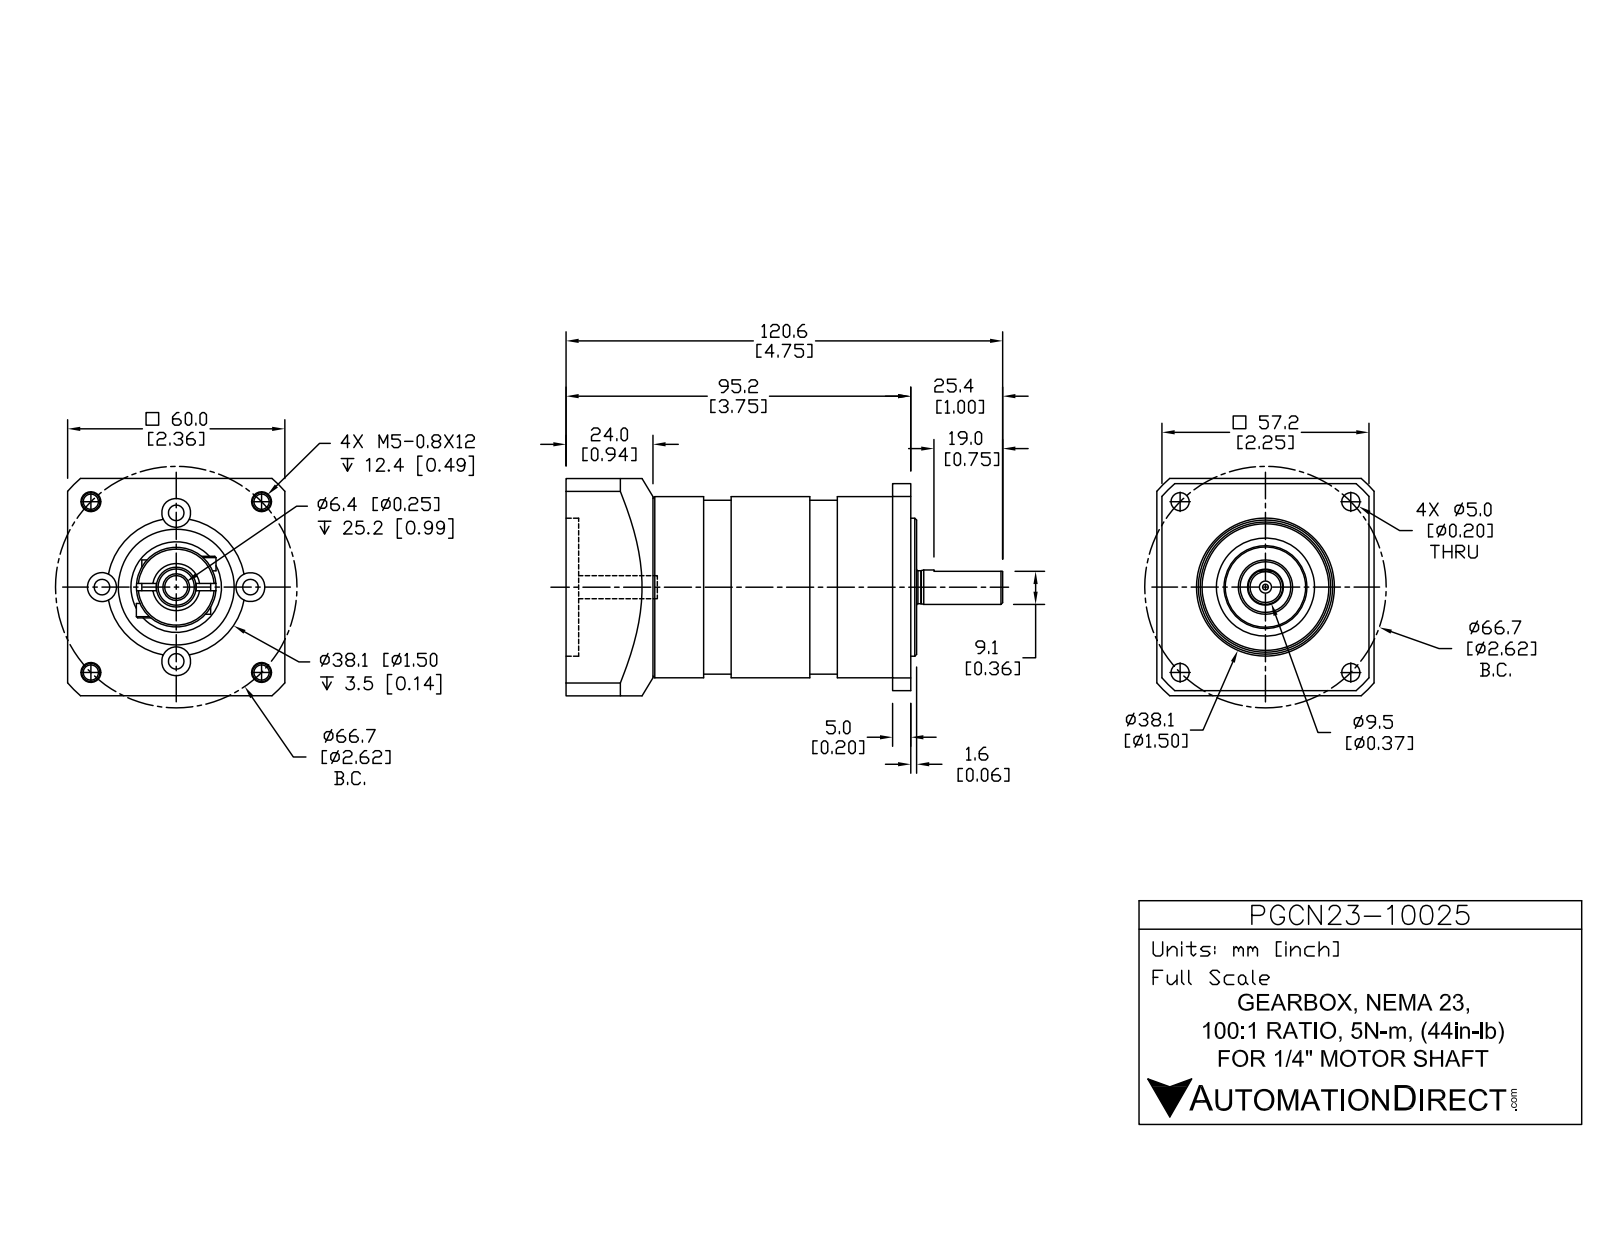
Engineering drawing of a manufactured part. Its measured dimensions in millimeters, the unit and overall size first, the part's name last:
Units: millimetres
Overall size (bounding box): 120.6 × 60 × 60
Round holes (diameter × count): ⌀4.2 ×4, ⌀4.3 ×4, ⌀5 ×4, ⌀8 ×4, ⌀4 ×2, ⌀9 ×2, ⌀1.6 ×1, ⌀6.4 ×1, ⌀11 ×1, ⌀25 ×1, ⌀27.1 ×1, ⌀32 ×1
Round bosses / shafts (diameter × count): ⌀7 ×2, ⌀50 ×1, ⌀48 ×1, ⌀22.9 ×1, ⌀22.2 ×1, ⌀22 ×1, ⌀15 ×1, ⌀9.5 ×1
Partial cylindrical surfaces — rounded edges, fillets, slot ends (radius × count): R4 ×2, R38 ×1, R40 ×1
Main face-to-face distances: 95.2, 60, 71.2, 24, 5, 66.2, 90.2, 3, 1.4, 58.6
Hole centre spacings: 23.8, 50, 20.5, 29, 33.3, 47.1, 1.3, 15
Volume: 204 800 mm³ · Surface area: 39 150 mm²
Bodies: 3 solids, 258 faces (71 planar, 118 cylindrical, 69 other)
Part name (STEP PRODUCT): PE-N23-II 11mm Input; N23-F03_1; Bushing_.25x11x14.9_1; PGCN23-10025
STEP written by: SolidWorks 2014 (AUTOMOTIVE_DESIGN)
